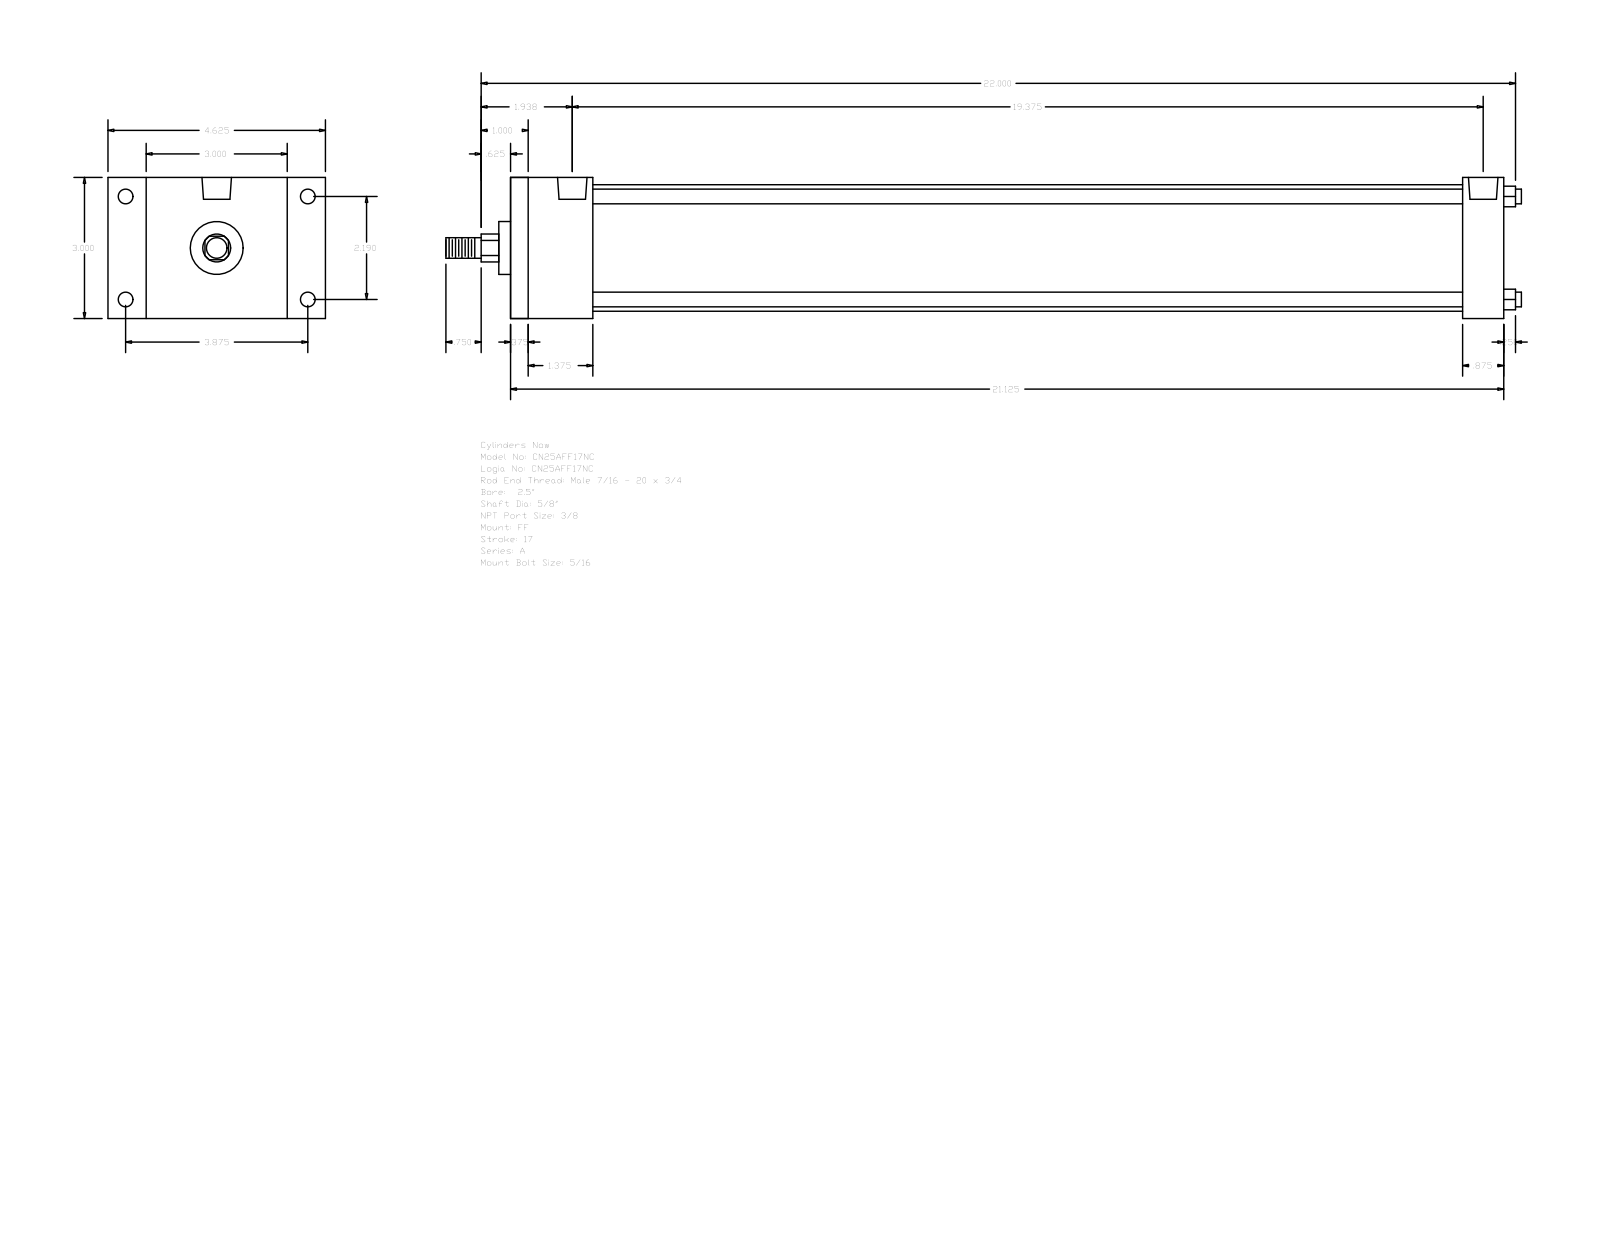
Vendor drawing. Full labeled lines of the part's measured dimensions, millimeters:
Part name (STEP PRODUCT): A_FF__0250_0.625
STEP written by: GSSL Pune (CONFIG_CONTROL_DESIGN)
Units: millimetres
Bodies: 0 solids, 92 faces (64 planar, 28 cylindrical, 0 other)
Overall size (bounding box): 581.02 × 117.47 × 76.2
Round holes (diameter × count): ⌀5.56 ×4, ⌀7.94 ×4, ⌀15.93 ×2
Round bosses / shafts (diameter × count): ⌀7.94 ×4, ⌀68.33 ×1, ⌀28.57 ×1, ⌀15.88 ×1, ⌀11.11 ×1
Partial cylindrical surfaces — rounded edges, fillets, slot ends (radius × count): R7.54 ×1
Main face-to-face distances: 76.2, 536.57, 9.52, 527.05, 44.45, 34.93, 514.35, 504.83, 469.9, 492.12
Hole centre spacings: 2.38, 55.62, 98.42, 113.05, 494.51, 496.89, 492.13
